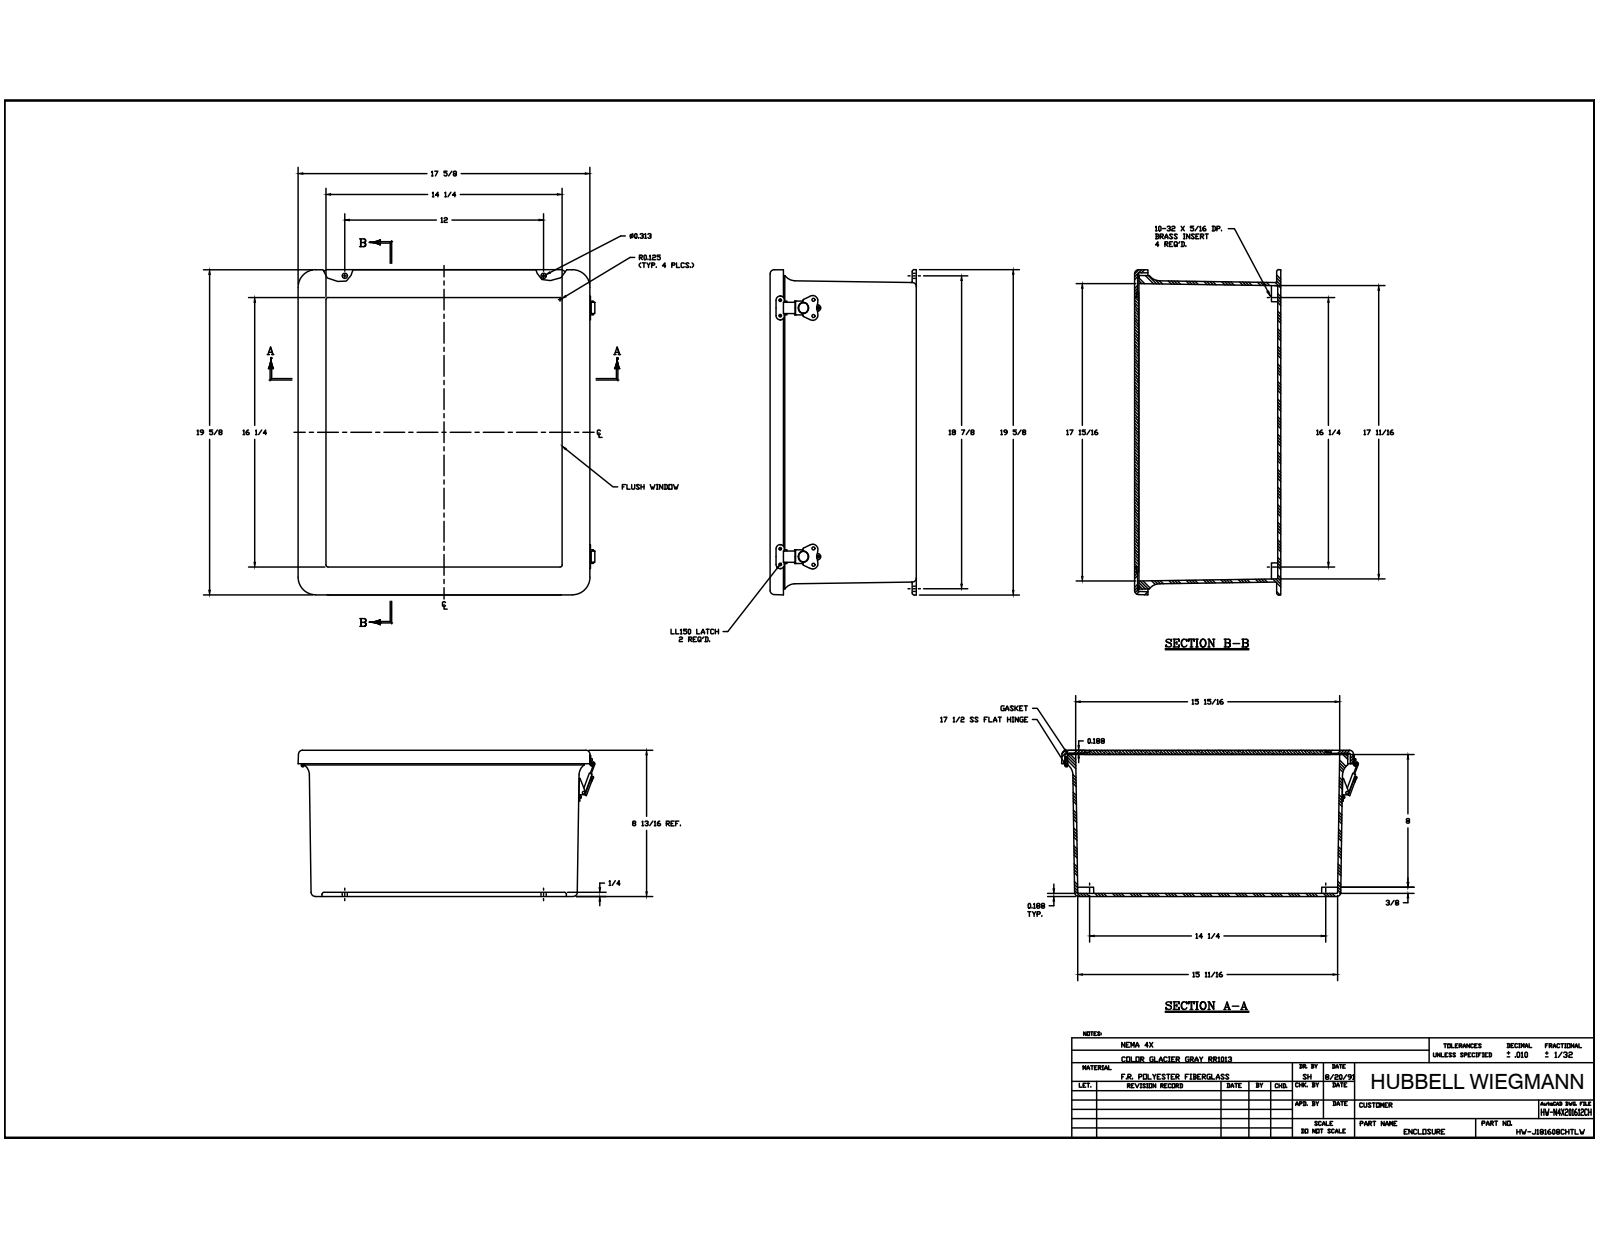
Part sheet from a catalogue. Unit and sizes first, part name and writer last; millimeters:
Units: millimetres
Overall size (bounding box): 498.48 × 455.08 × 223.82
Round holes (diameter × count): ⌀3.56 ×20, ⌀3.33 ×12, ⌀3.86 ×5, ⌀3.3 ×4, ⌀3.96 ×4, ⌀4.2 ×4, ⌀5 ×4, ⌀5.54 ×4, ⌀3 ×2, ⌀3.5 ×2, ⌀4.61 ×2, ⌀4.62 ×2
Round bosses / shafts (diameter × count): ⌀6.35 ×20, ⌀3.17 ×20, ⌀6.86 ×4, ⌀14.8 ×2, ⌀13.3 ×2, ⌀5.3 ×2, ⌀4.7 ×2, ⌀3.25 ×2
Partial cylindrical surfaces — rounded edges, fillets, slot ends (radius × count): R0.79 ×20, R2 ×19, R3.17 ×16, R6.35 ×12, R0.95 ×8, R1 ×8, R1.15 ×8, R1.2 ×8
Main face-to-face distances: 4.76, 223.82, 4.77, 6.35, 217.47, 219.05, 212.7, 219.06, 214.29, 1.59
Hole centre spacings: 380.6, 85.72, 85.73, 171.45, 6.36, 20.99, 380.59, 247.65
Volume: 4 522 000 mm³ · Surface area: 1 802 000 mm²
Bodies: 53 solids, 1326 faces (614 planar, 517 cylindrical, 195 other)
Part name (STEP PRODUCT): J1816HL_3; RMINS45821P_113; RMINS45821P_114; RMINS45821P_115 (+8 more)
STEP written by: Autodesk Inventor 2014 (AUTOMOTIVE_DESIGN)
